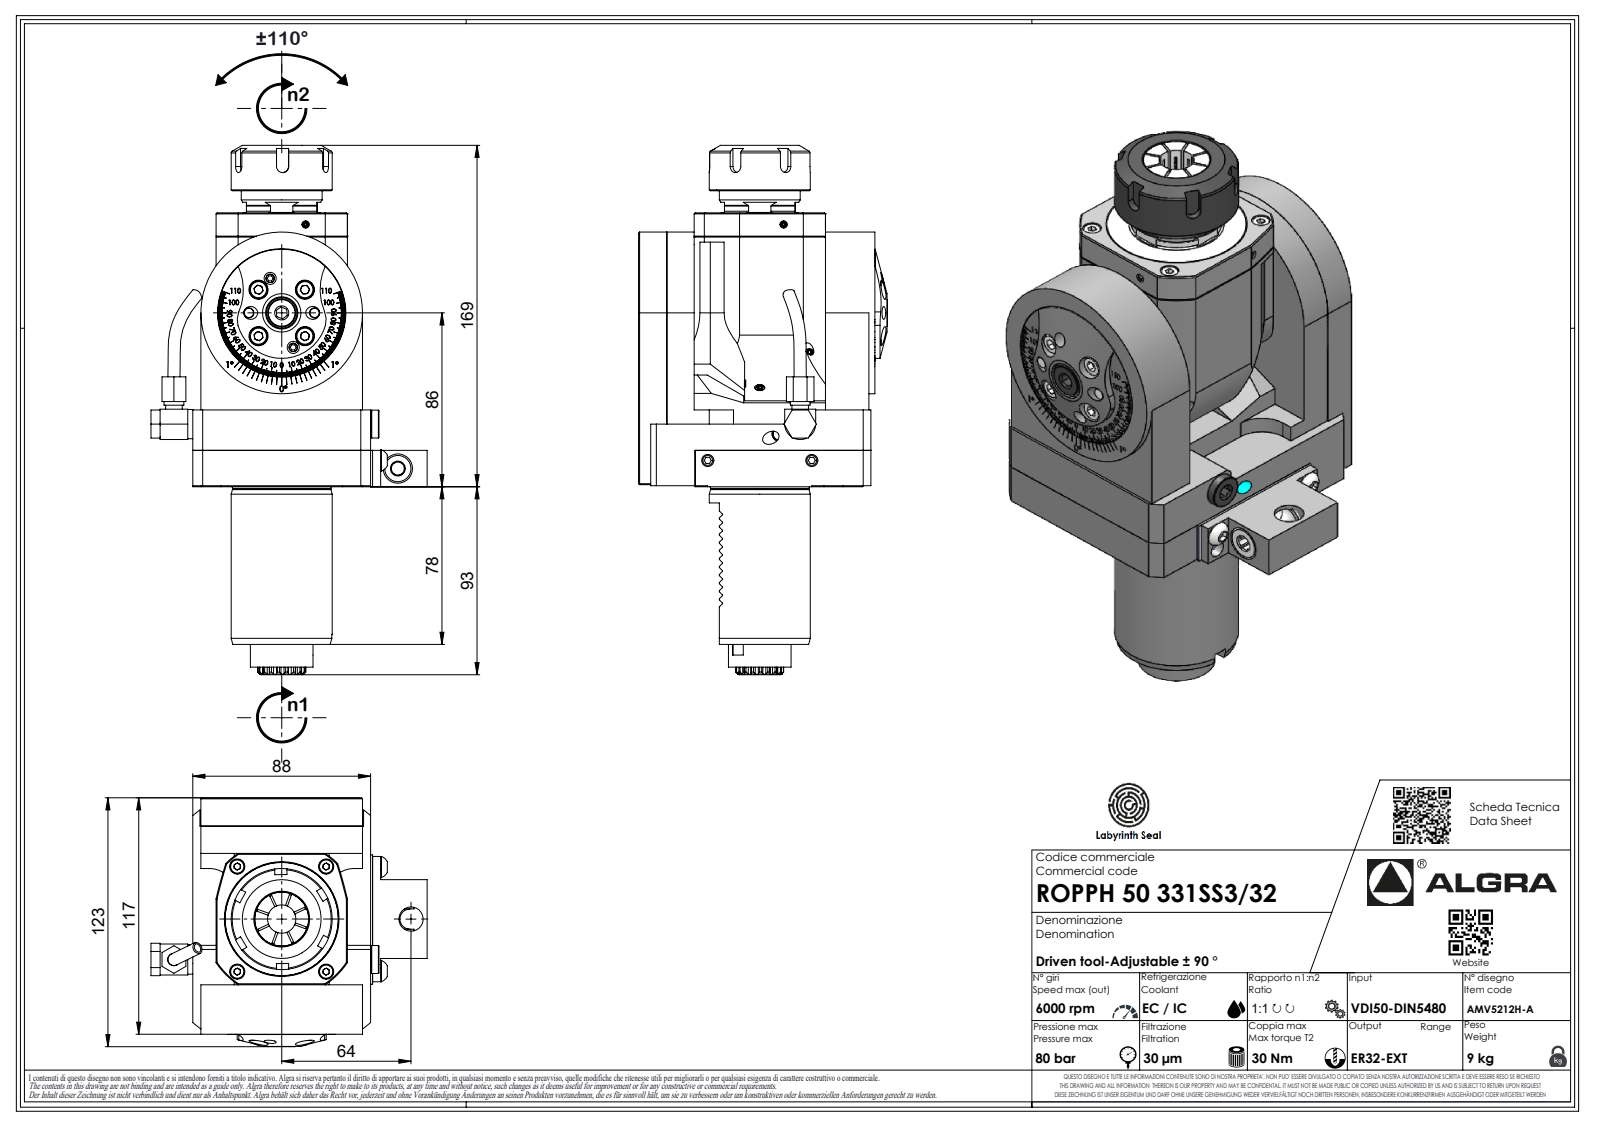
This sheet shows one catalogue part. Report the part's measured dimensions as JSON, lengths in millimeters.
{"part_name": "ROPPH50331SS332", "step_written_by": "SolidWorks 2023 (AUTOMOTIVE_DESIGN)", "units": "millimeters", "bodies": {"solids": 1, "faces": 767, "planar": 421, "cylindrical": 150, "other": 196}, "overall_size": [261.91, 136.7, 123], "volume_mm3": 1279000, "surface_area_mm2": 111521, "round_holes": [[2.1, 1], [31, 1]], "round_bosses_or_shafts": [[80, 1], [50, 1], [48.7, 1], [40, 1], [14.5, 1], [9.8, 1], [8.2, 1], [6.37, 1]], "partial_cylinders_radius": [[1.61, 36], [0.3, 12], [0.33, 7], [0.52, 7], [3.7, 7], [3, 5], [10, 2], [12, 2]], "face_to_face_distances": [4, 65, 84, 0.5, 11.5, 72.5, 76.5, 7.5, 27.5, 89.5]}
